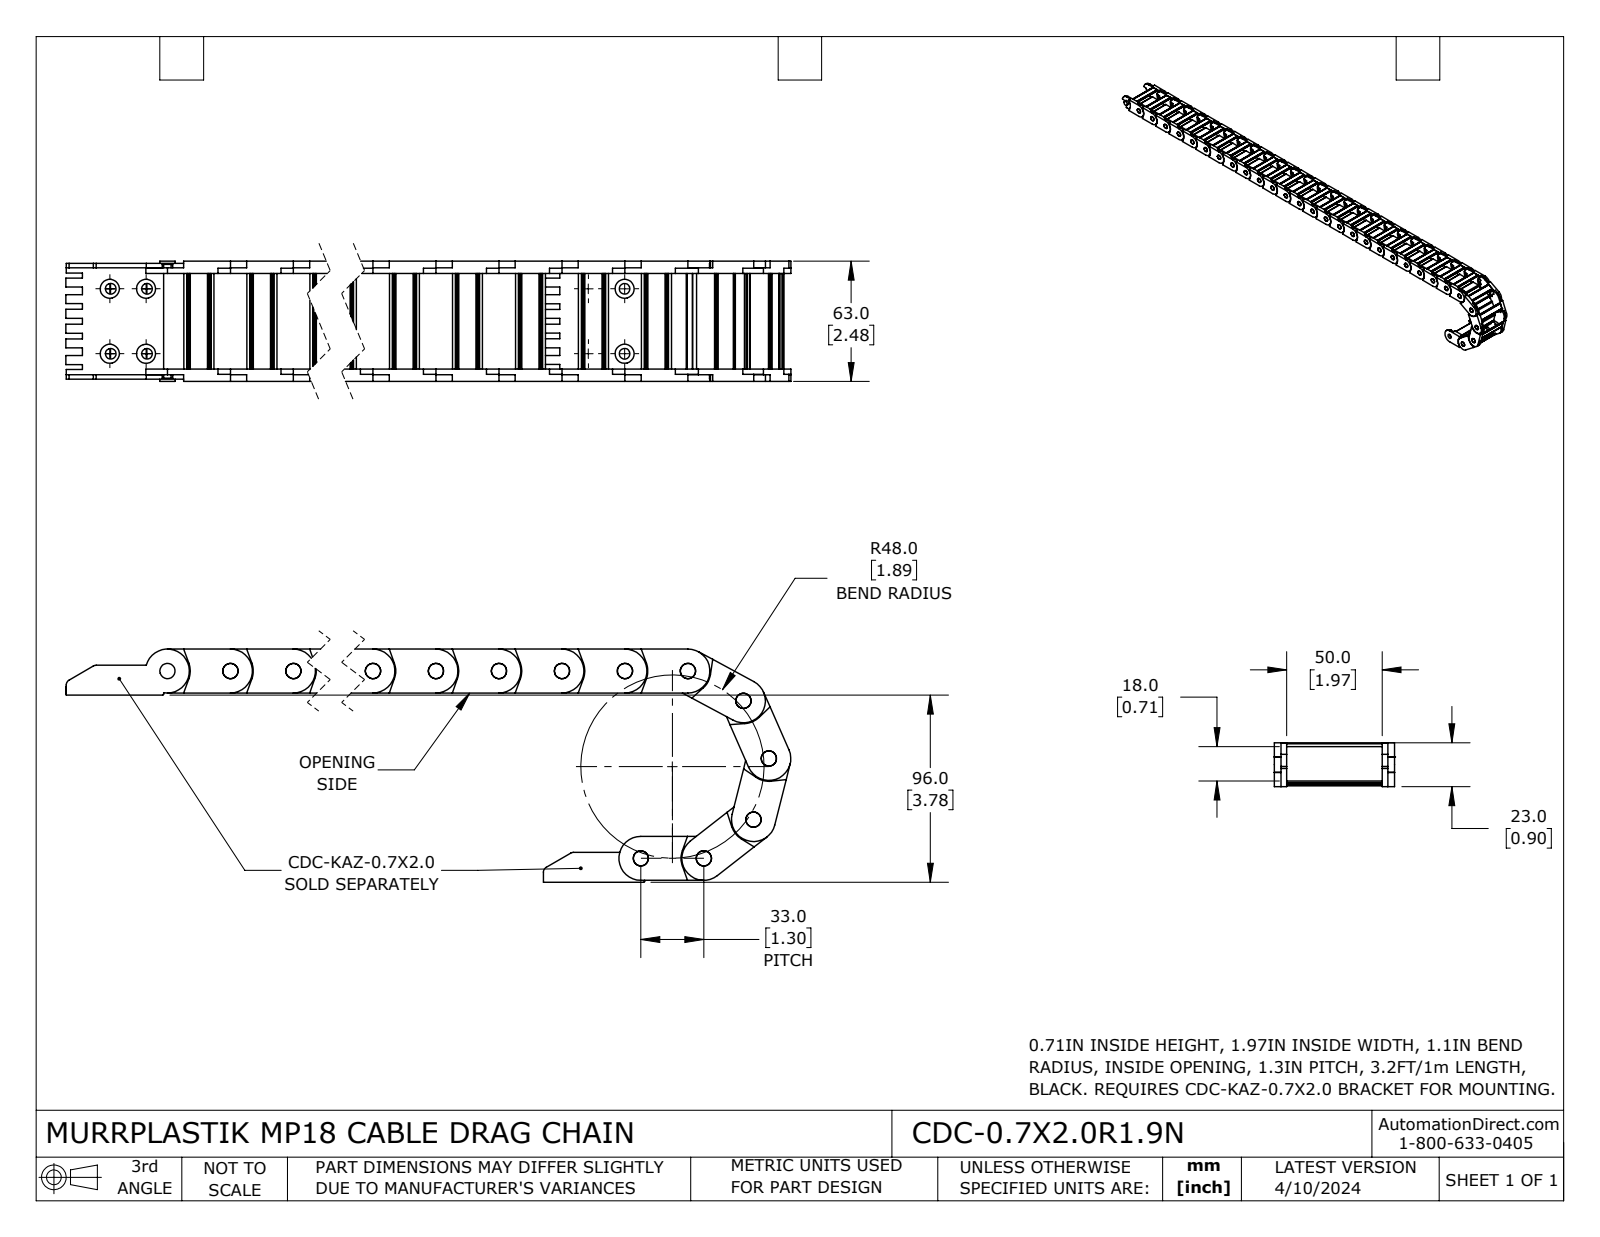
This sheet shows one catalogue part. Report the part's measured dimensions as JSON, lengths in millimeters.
{"part_name": "CDC-0.7X2.0R1.9N", "step_written_by": "SolidWorks 2023 (CONFIG_CONTROL_DESIGN)", "units": "millimeters", "bodies": {"solids": 30, "faces": 2370, "planar": 1110, "cylindrical": 1260, "other": 0}, "overall_size": [890.23, 121.09, 63], "volume_mm3": 345175, "surface_area_mm2": 267172, "round_holes": [[8, 30]], "round_bosses_or_shafts": [[8, 1]], "partial_cylinders_radius": [[0.5, 120], [1.5, 120], [0.2, 60], [0.3, 60], [11.5, 31], [11.95, 31], [5, 30], [5.45, 30]], "face_to_face_distances": [6.5, 56.5, 63, 2, 3.5, 59.5, 3, 53, 3.7, 59.3], "hole_center_spacings": [33, 66, 99, 132, 165, 198, 231, 264]}
